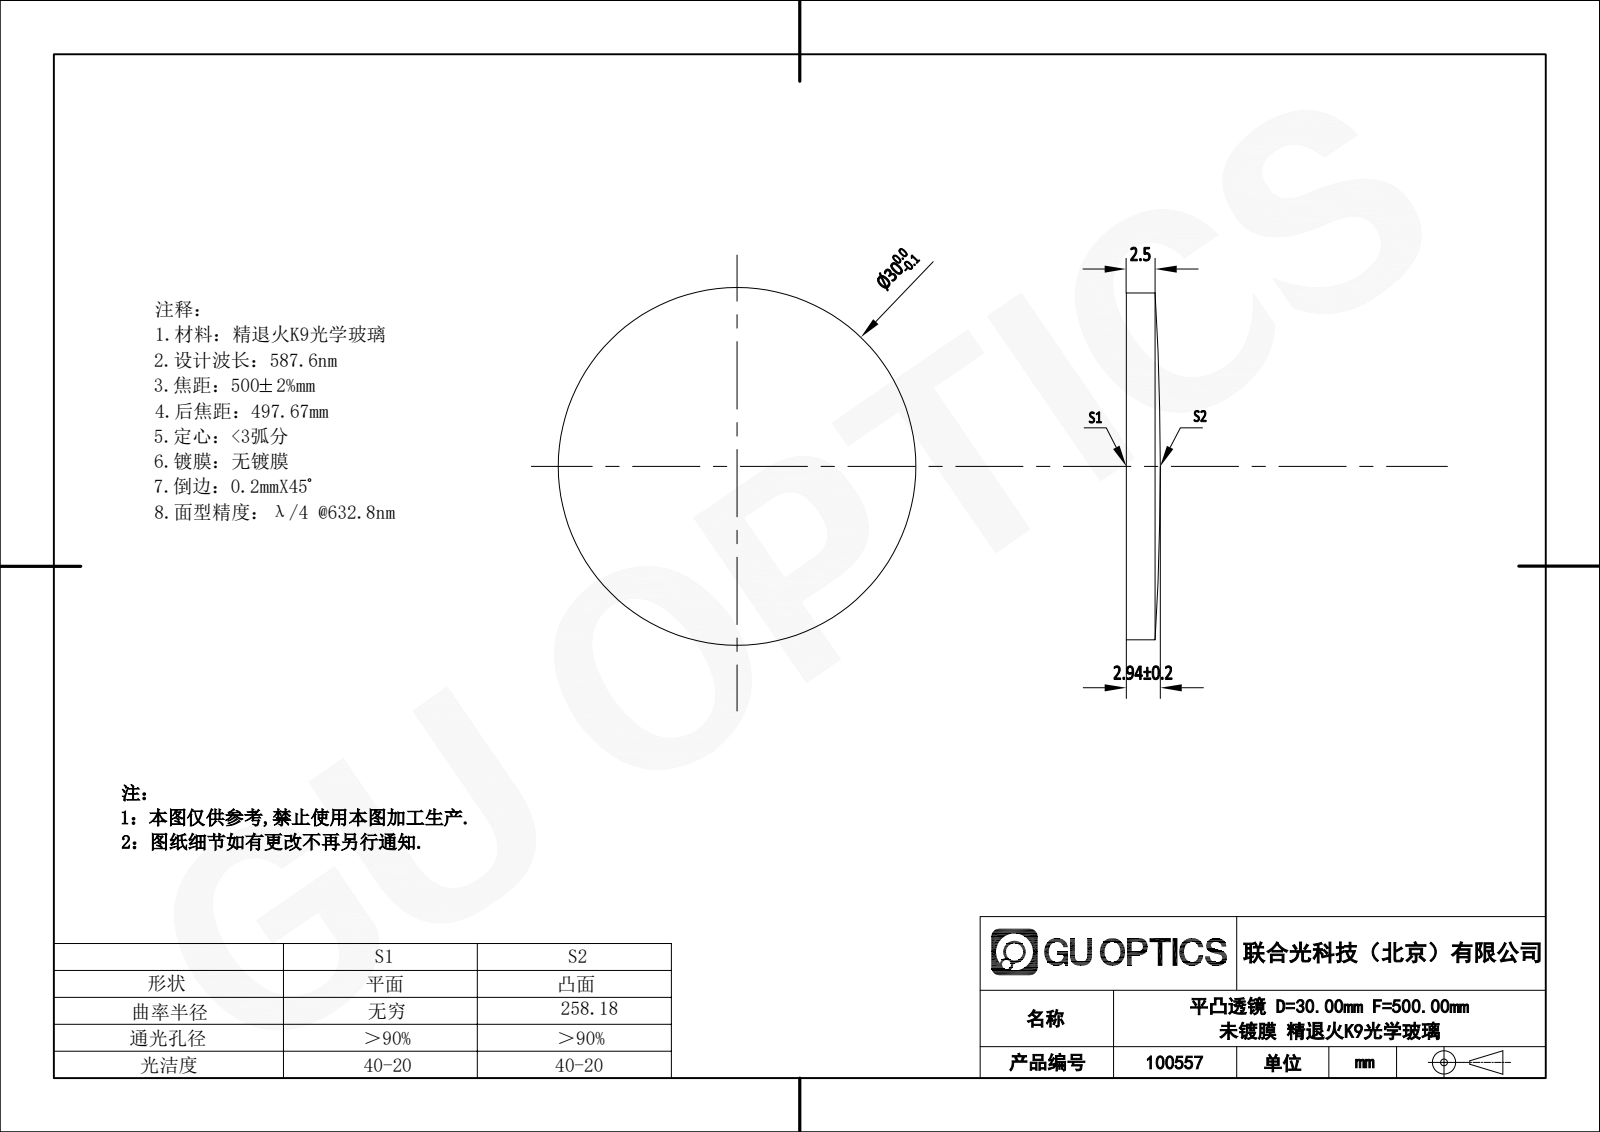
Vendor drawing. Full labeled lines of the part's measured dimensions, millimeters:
Part name (STEP PRODUCT): 100557
STEP written by: SolidWorks 2020 (CONFIG_CONTROL_DESIGN)
Units: millimetres
Bodies: 1 solid, 5 faces (1 planar, 2 cylindrical, 2 other)
Overall size (bounding box): 30 × 30 × 2.94
Volume: 1 922 mm³ · Surface area: 1 650 mm²
Round bosses / shafts (diameter × count): ⌀30 ×1
